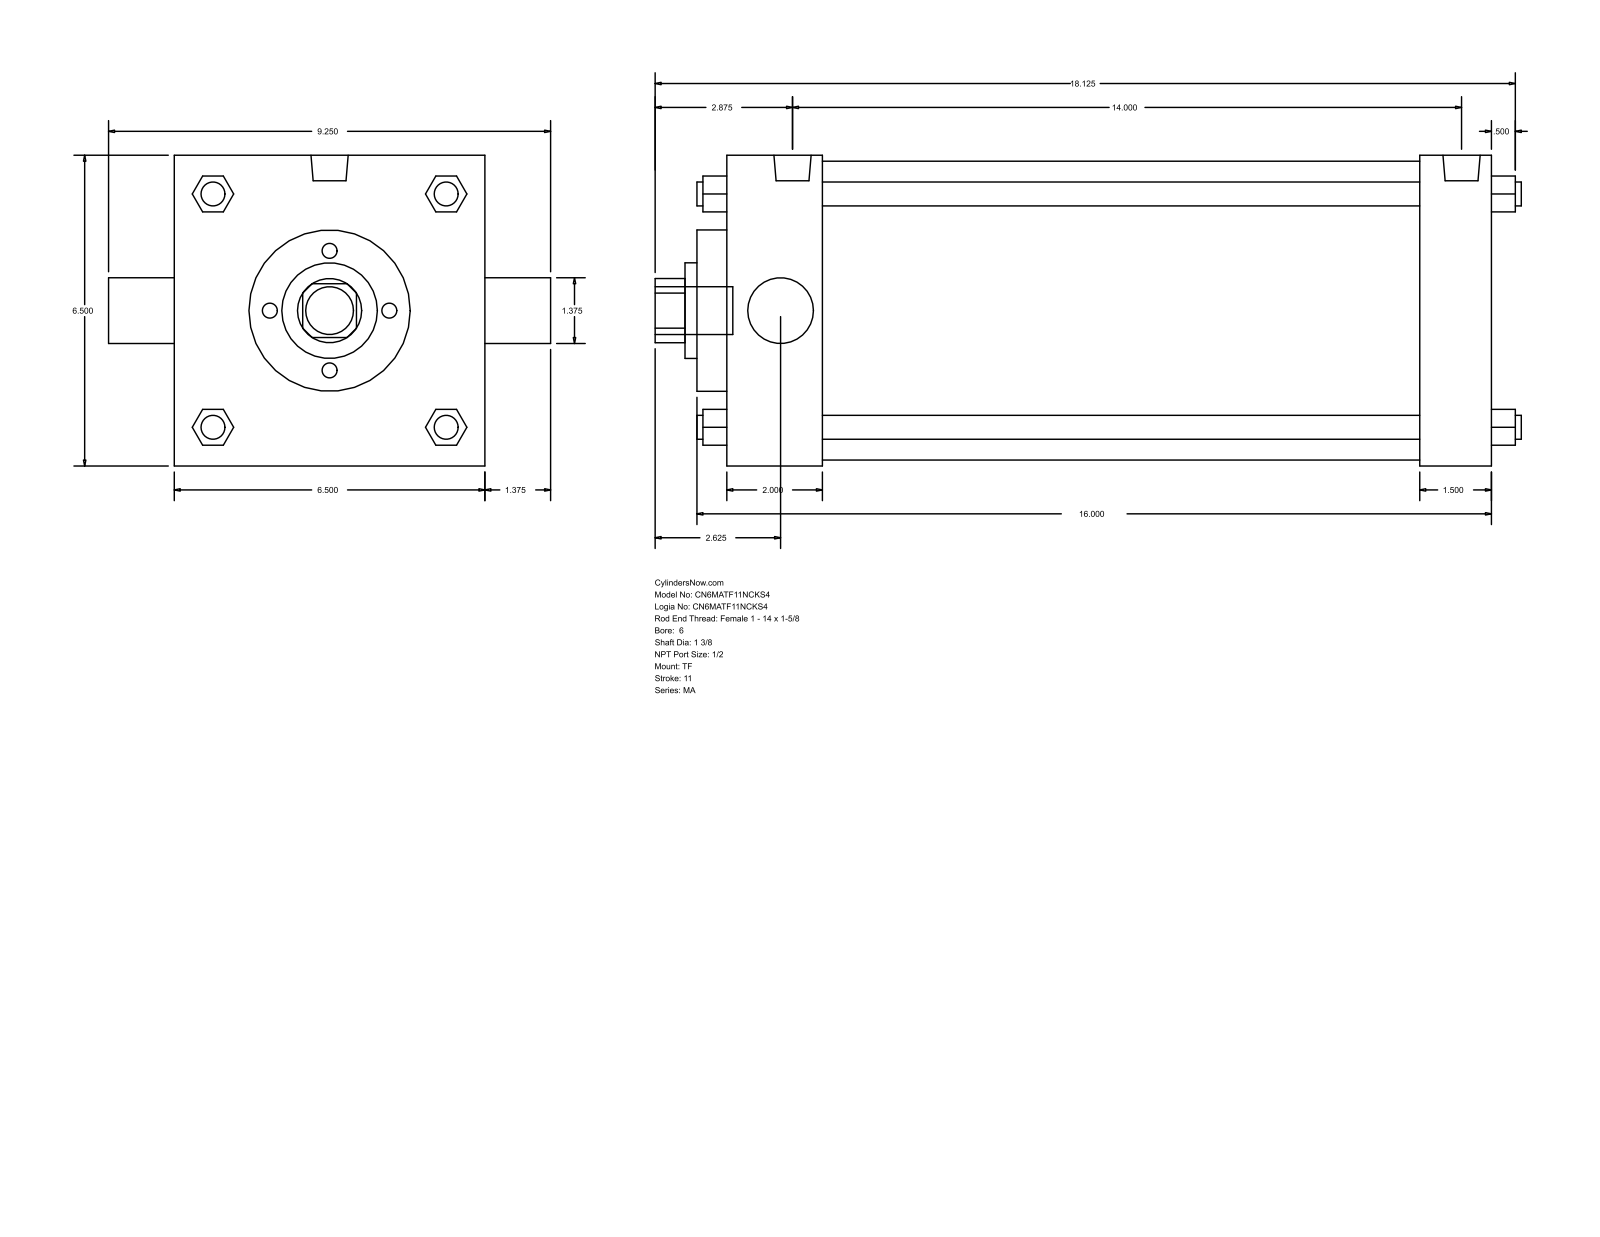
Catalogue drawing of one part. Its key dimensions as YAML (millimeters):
part_name: "MA_TF__0600_1.375"
step_written_by: "GSSL Pune (CONFIG_CONTROL_DESIGN)"
units: millimeters
bodies: {solids: 0, faces: 122, planar: 93, cylindrical: 29, other: 0}
overall_size: [460.38, 234.95, 165.1]
round_holes:
  - {diameter: 34.92, count: 2}
  - {diameter: 50.8, count: 1}
  - {diameter: 85.72, count: 1}
  - {diameter: 158.75, count: 1}
round_bosses_or_shafts:
  - {diameter: 12.7, count: 4}
  - {diameter: 17.46, count: 3}
  - {diameter: 19.77, count: 2}
  - {diameter: 25.4, count: 1}
partial_cylinders:
  - {radius: 17.06, count: 1}
face_to_face_distances: [165.1, 409.58, 50.8, 358.78, 371.47, 320.67, 38.11, 15.87, 66.67, 387.34]
